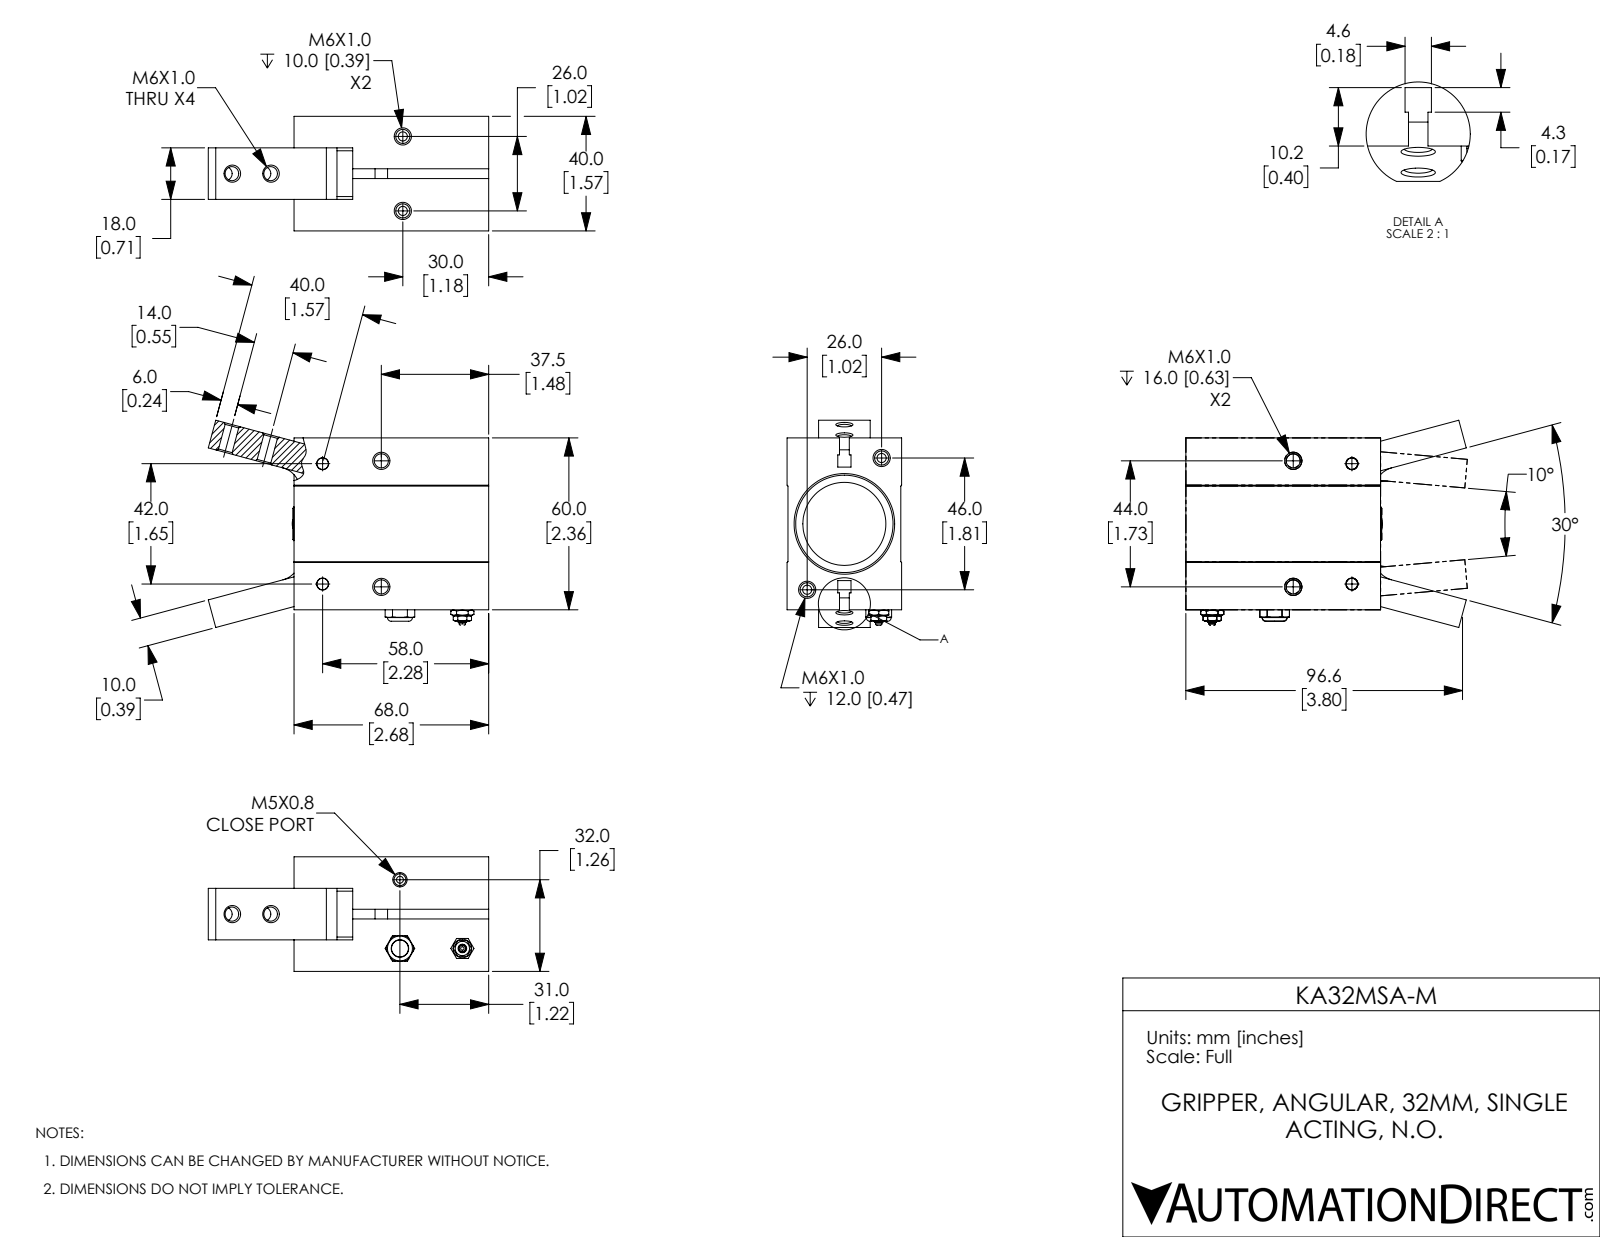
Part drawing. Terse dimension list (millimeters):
name: KA32MSA-M; KA32MSA-M-4; KA32MSA-M-3; KA32MSA-M-2 (+1 more)
written by: SolidWorks 2017 (AUTOMOTIVE_DESIGN)
unit: mm
bodies: 4 solids, 298 faces (120 planar, 90 cylindrical, 88 other)
size: 97.93 × 72.36 × 40
volume: 133 806 mm³; area: 43 599 mm²
holes: 6× ⌀4.92, 4× ⌀4.92, 2× ⌀4, 2× ⌀4.13, 2× ⌀6.2, 1× ⌀3, 1× ⌀16, 1× ⌀29, 1× ⌀32, 1× ⌀34, 1× ⌀35
bosses: 1× ⌀31.5, 1× ⌀15, 1× ⌀10, 1× ⌀8.7, 1× ⌀3, 1× ⌀2.2
rounds: 2× R5, 2× R8
face distances: 10.7, 39.7, 11, 29, 28.7, 18, 40, 60, 39.4, 10
hole spacings: 1.41, 14, 20.52, 21.9, 25.02, 26.42, 34.6, 47.64
